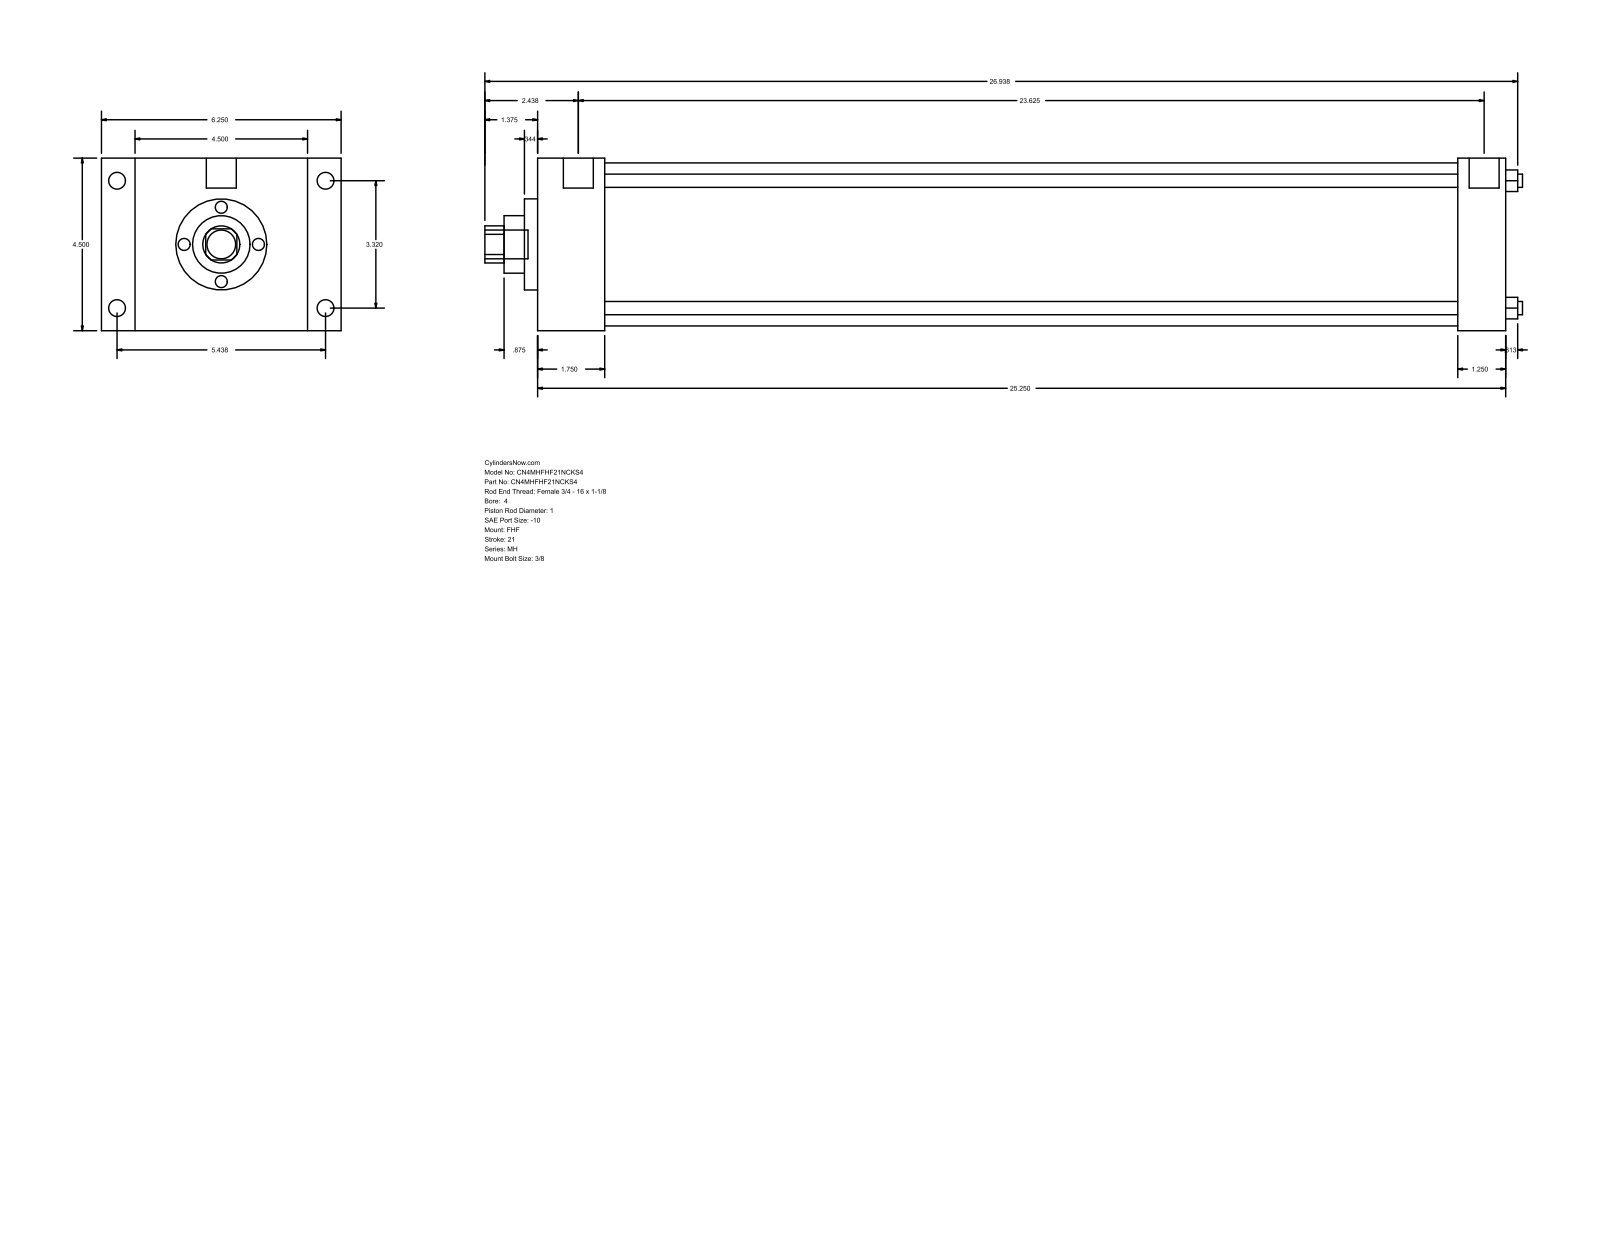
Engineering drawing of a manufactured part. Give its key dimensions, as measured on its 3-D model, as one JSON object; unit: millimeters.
{"part_name": "MH_FHF__0400_1", "step_written_by": "GSSL Pune (CONFIG_CONTROL_DESIGN)", "units": "millimeters", "bodies": {"solids": 0, "faces": 90, "planar": 61, "cylindrical": 29, "other": 0}, "overall_size": [687.39, 158.75, 114.3], "round_holes": [[8.76, 4], [25.4, 1], [38.1, 1], [60.33, 1], [107.95, 1]], "round_bosses_or_shafts": [[11.13, 4], [8.73, 4], [19.84, 2], [19.05, 1]], "partial_cylinders_radius": [[12.29, 1]], "face_to_face_distances": [114.3, 641.35, 44.46, 596.89, 22.23, 136.53, 158.76, 609.6, 565.14, 31.75], "hole_center_spacings": [59.62, 84.32, 119.25]}
